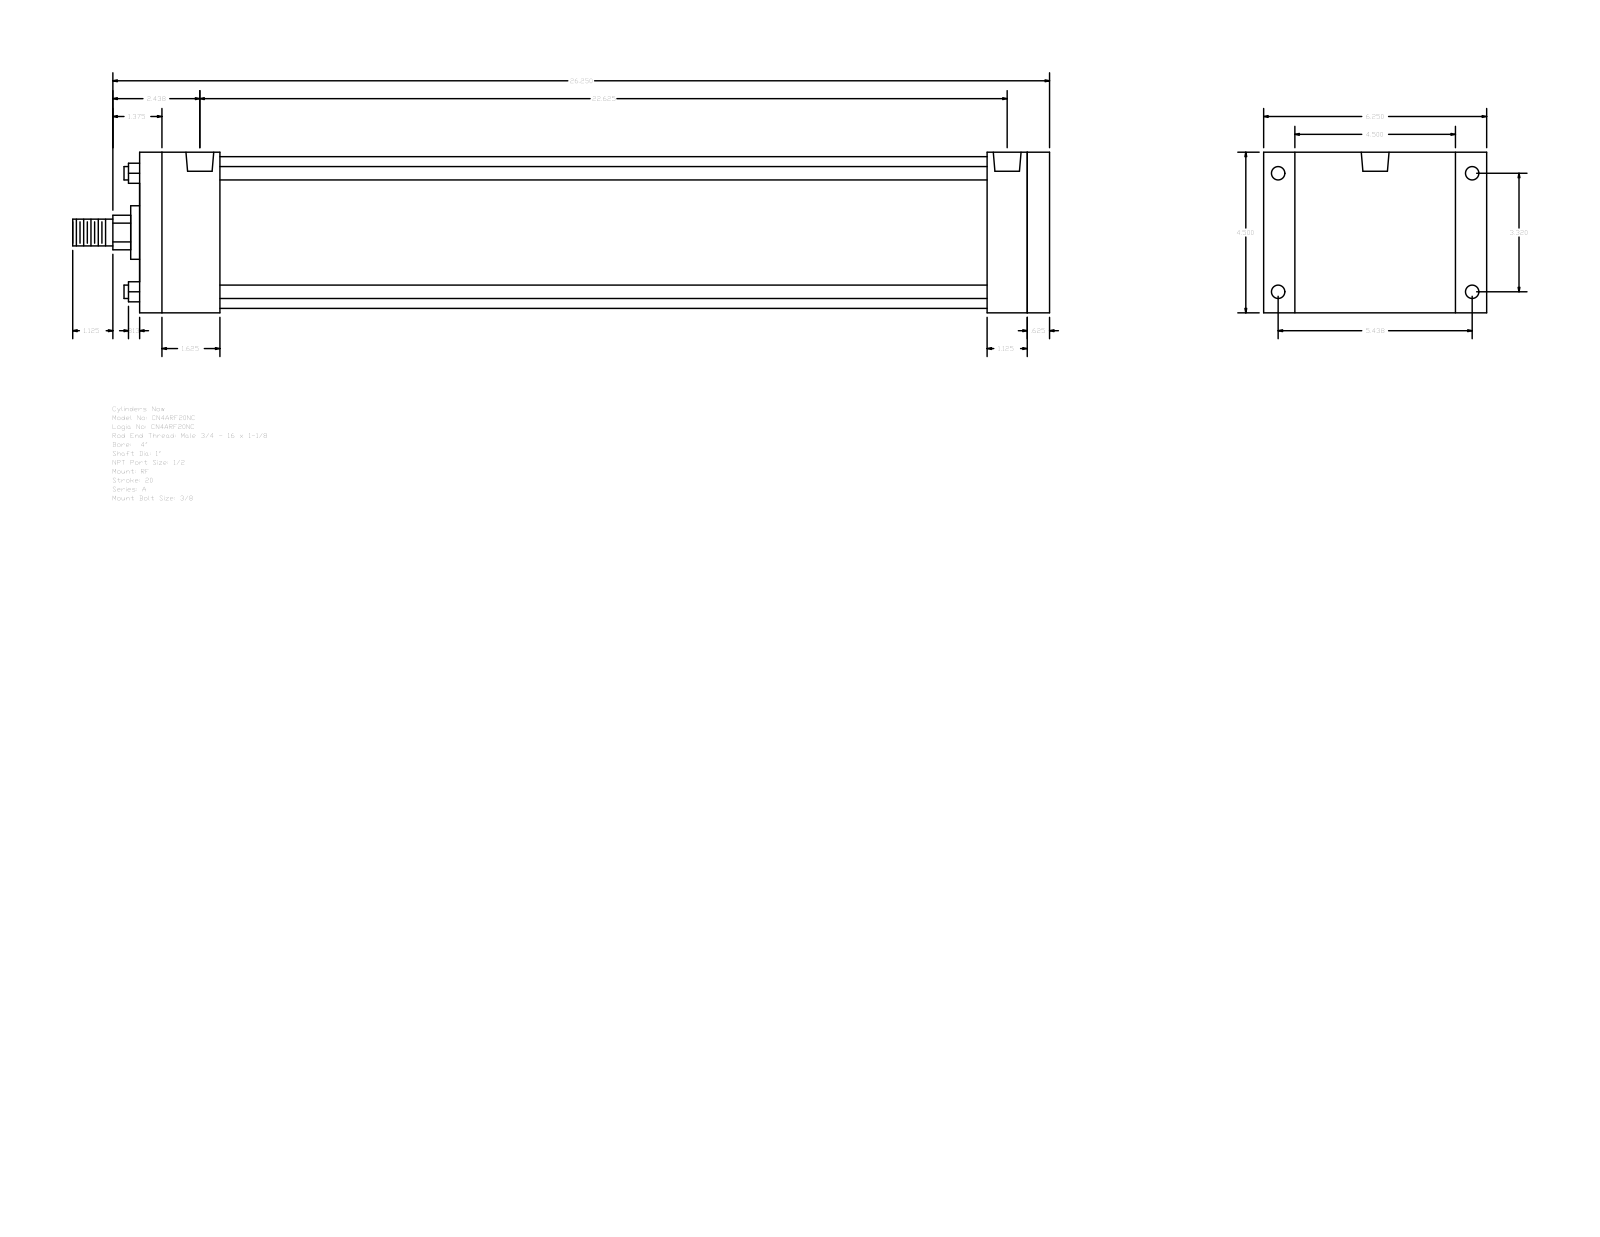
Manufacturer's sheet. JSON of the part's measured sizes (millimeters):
{"part_name": "A_RF__0400_1", "step_written_by": "GSSL Pune (CONFIG_CONTROL_DESIGN)", "units": "millimeters", "bodies": {"solids": 0, "faces": 92, "planar": 64, "cylindrical": 28, "other": 0}, "overall_size": [695.33, 158.75, 114.3], "round_holes": [[8.73, 4], [9.53, 4], [19.77, 2]], "round_bosses_or_shafts": [[9.53, 4], [107.95, 1], [38.1, 1], [25.4, 1], [19.05, 1]], "partial_cylinders_radius": [[12.29, 1]], "face_to_face_distances": [114.3, 647.7, 631.83, 15.87, 22.23, 136.53, 603.25, 28.58, 44.45, 57.15], "hole_center_spacings": [3.18, 84.32, 138.12, 161.82, 568.32, 571.5, 574.68]}
